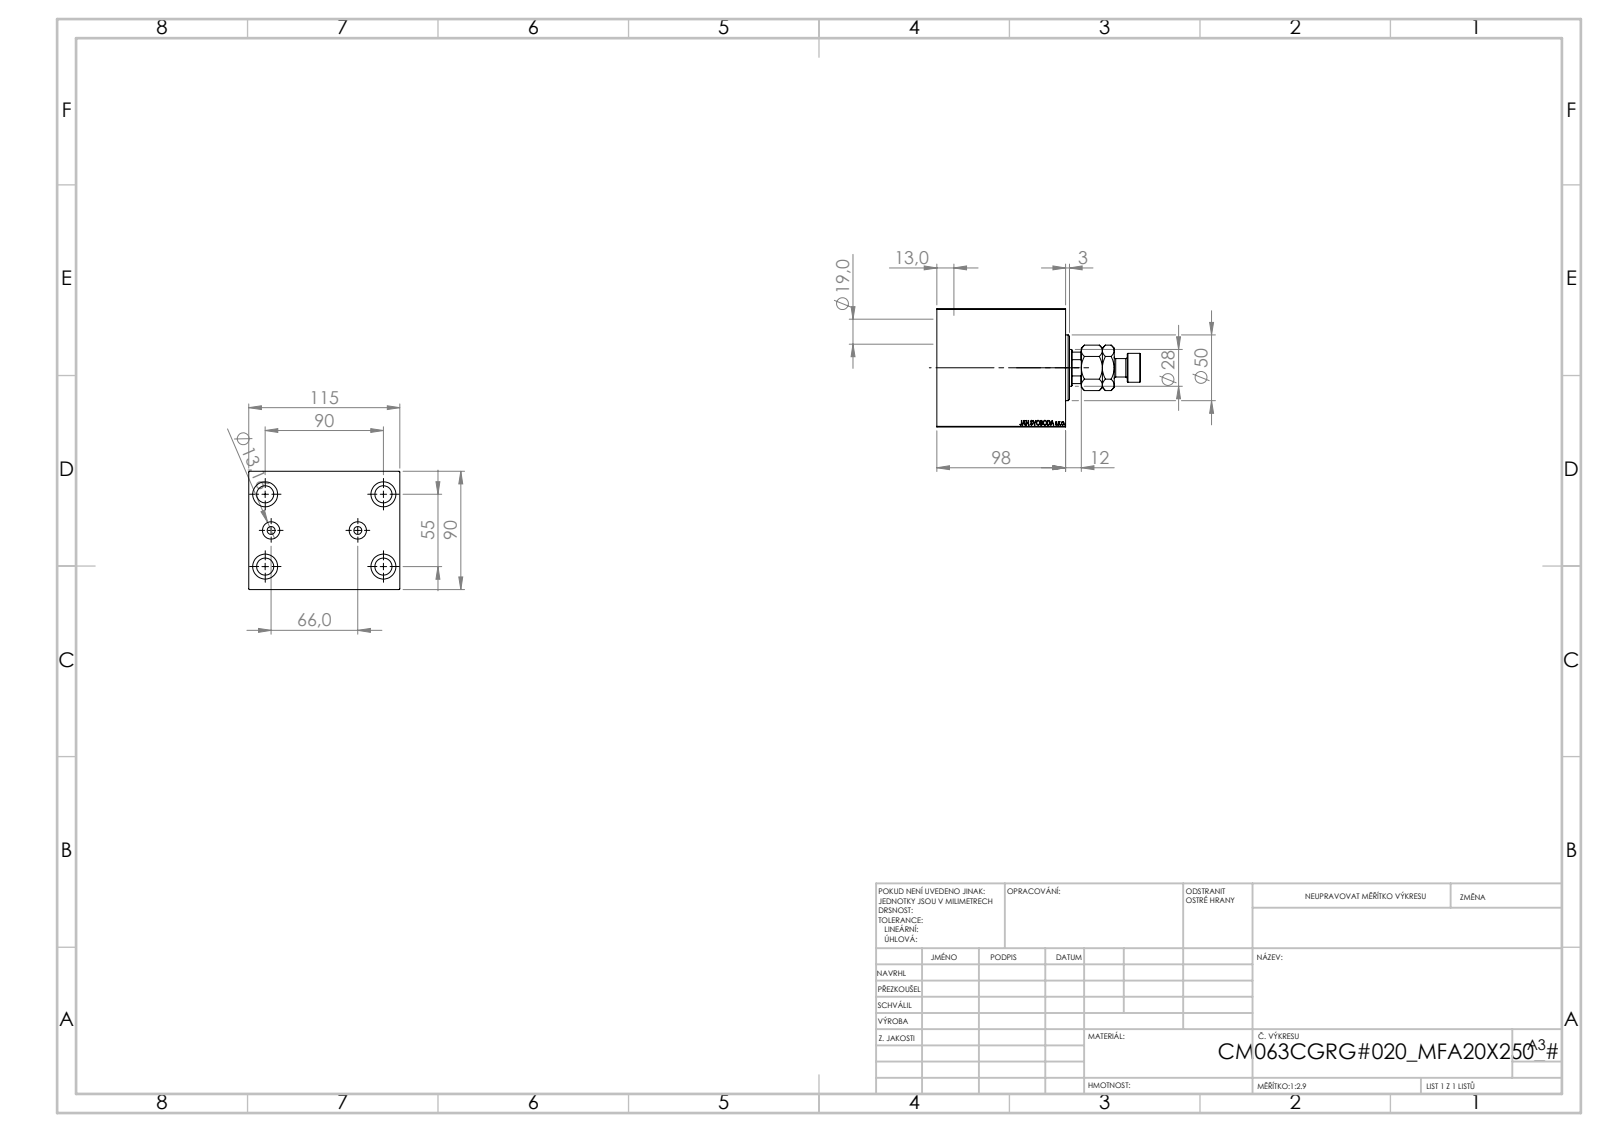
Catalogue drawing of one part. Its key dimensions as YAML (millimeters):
part_name: "V450CM_VC_B; V450CM_C_Body; V450CM_C_VCP; MFA"
step_written_by: "SolidWorks 2019 (CONFIG_CONTROL_DESIGN)"
units: millimeters
bodies: {solids: 4, faces: 913, planar: 425, cylindrical: 62, other: 426}
overall_size: [156.5, 115, 90]
volume: 918270
surface_area: 122017
round_holes:
  - {diameter: 13, count: 4}
  - {diameter: 19, count: 4}
  - {diameter: 6, count: 2}
  - {diameter: 13.16, count: 2}
  - {diameter: 18.5, count: 1}
  - {diameter: 28, count: 1}
  - {diameter: 31.5, count: 1}
  - {diameter: 63, count: 1}
  - {diameter: 65, count: 1}
  - {diameter: 72, count: 1}
round_bosses_or_shafts:
  - {diameter: 50, count: 1}
  - {diameter: 22, count: 1}
  - {diameter: 14, count: 1}
partial_cylinders:
  - {radius: 13.5, count: 1}
face_to_face_distances: [90, 115, 98, 48.5, 49.5, 88, 30, 10, 5, 39.5]
hole_center_spacings: [30, 52.74, 82.71, 33, 55, 90, 105.48, 66]
